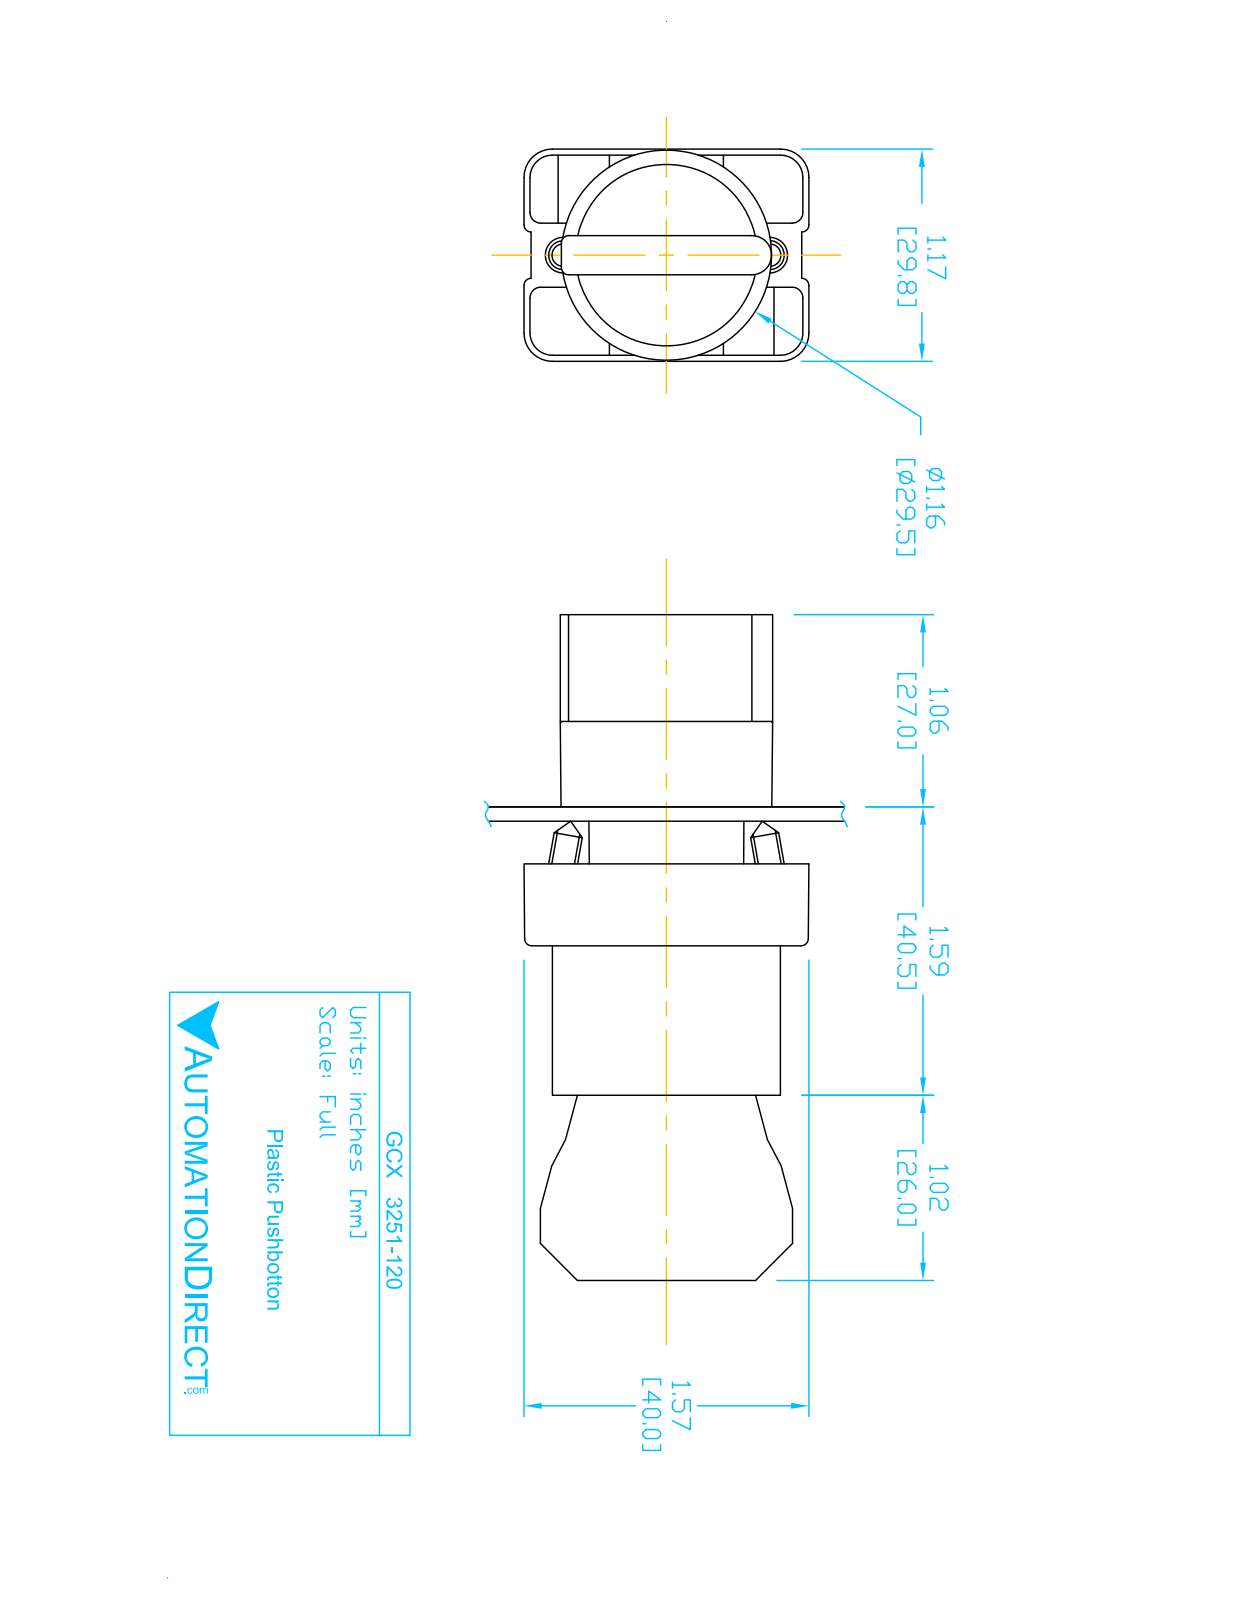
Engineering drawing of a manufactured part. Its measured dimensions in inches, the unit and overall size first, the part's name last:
Units: inches
Overall size (bounding box): 3.653 × 1.581 × 1.177
Round holes (diameter × count): ⌀0.079 ×2, ⌀0.124 ×2, ⌀0.13 ×2, ⌀0.087 ×1, ⌀0.197 ×1, ⌀0.469 ×1, ⌀0.878 ×1, ⌀0.888 ×1, ⌀1.024 ×1
Round bosses / shafts (diameter × count): ⌀0.157 ×4, ⌀1.175 ×1, ⌀1.004 ×1, ⌀0.945 ×1, ⌀0.856 ×1, ⌀0.78 ×1, ⌀0.504 ×1
Partial cylindrical surfaces — rounded edges, fillets, slot ends (radius × count): R0.059 ×24, R0.041 ×12, R0.124 ×12, R0.157 ×12, R0.039 ×9, R0.128 ×2, R0.02 ×1, R0.063 ×1
Main face-to-face distances: 0.827, 2.02, 1.193, 0.579, 1.244, 1.171, 0.472, 0.469, 0.031, 0.033
Hole centre spacings: 0.236, 0.544, 0.472, 0.49
Volume: 2.799 in³ · Surface area: 39 in²
Bodies: 8 solids, 445 faces (263 planar, 151 cylindrical, 31 other)
Part name (STEP PRODUCT): ecx1040; ECX1050; GCX3251-120; GCX3251 OPERATOR (+1 more)
STEP written by: SolidWorks 2016 (AUTOMOTIVE_DESIGN)
